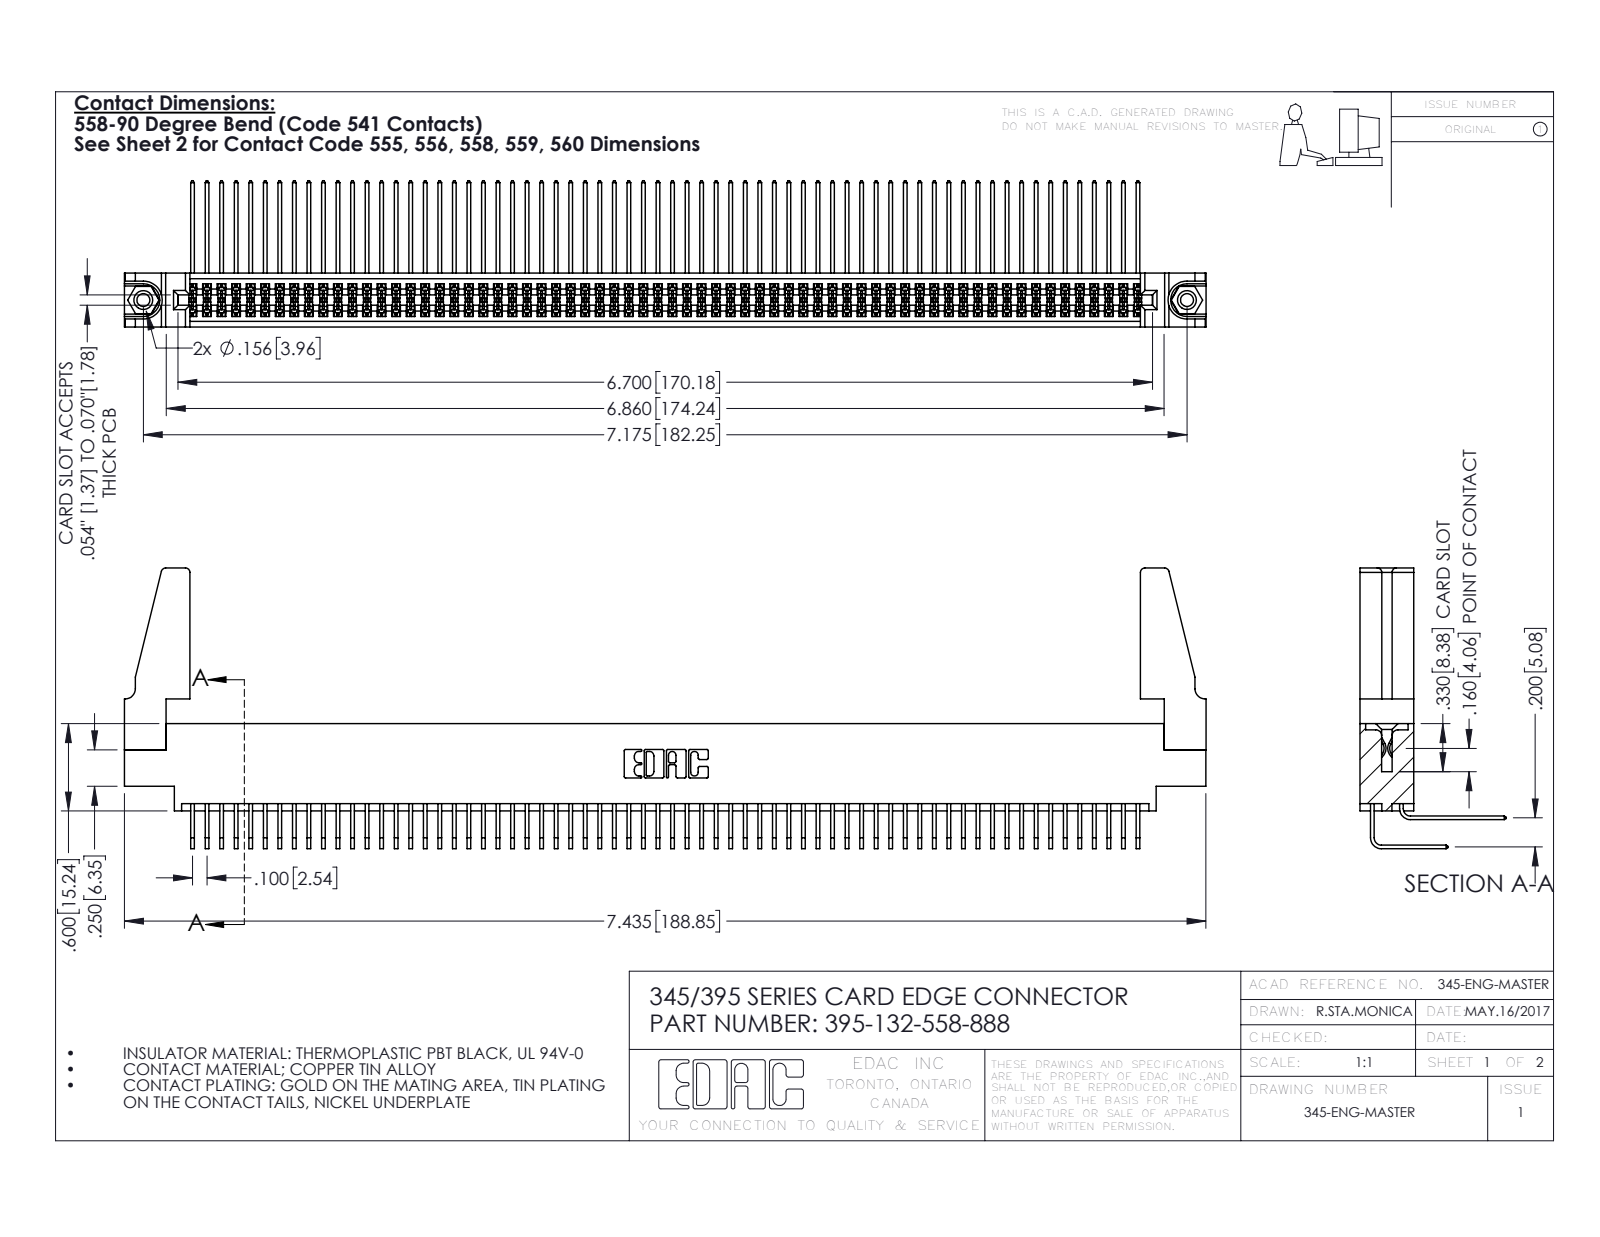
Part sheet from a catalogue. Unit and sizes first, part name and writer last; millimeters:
Units: millimetres
Overall size (bounding box): 188.9 × 49 × 25.5
Round holes (diameter × count): ⌀2.3 ×2, ⌀3.2 ×2, ⌀4 ×2, ⌀1.6 ×1
Round bosses / shafts (diameter × count): ⌀3.9 ×2
Partial cylindrical surfaces — rounded edges, fillets, slot ends (radius × count): R0.2 ×198, R0.3 ×22, R0.8 ×8, R0.2 ×6, R0.8 ×6, R0.7 ×3, R0.4 ×2, R0.5 ×2
Main face-to-face distances: 1.8, 7.6, 5.1, 9.4, 2.5, 6.9, 0.6, 5.7, 4.4, 0.6
Hole centre spacings: 6.9, 176.3, 182.2
Volume: 22 470 mm³ · Surface area: 35 720 mm²
Bodies: 137 solids, 7118 faces (4776 planar, 2326 cylindrical, 16 other)
Part name (STEP PRODUCT): 395-132-558-888; 345 Part_0.170 Offset - 0.156 Dia-TH; 345-292-001_558 559 Tail - 1; 345-292-001_558 Tail - 2 (+2 more)
STEP written by: SolidWorks 2016 (CONFIG_CONTROL_DESIGN)
